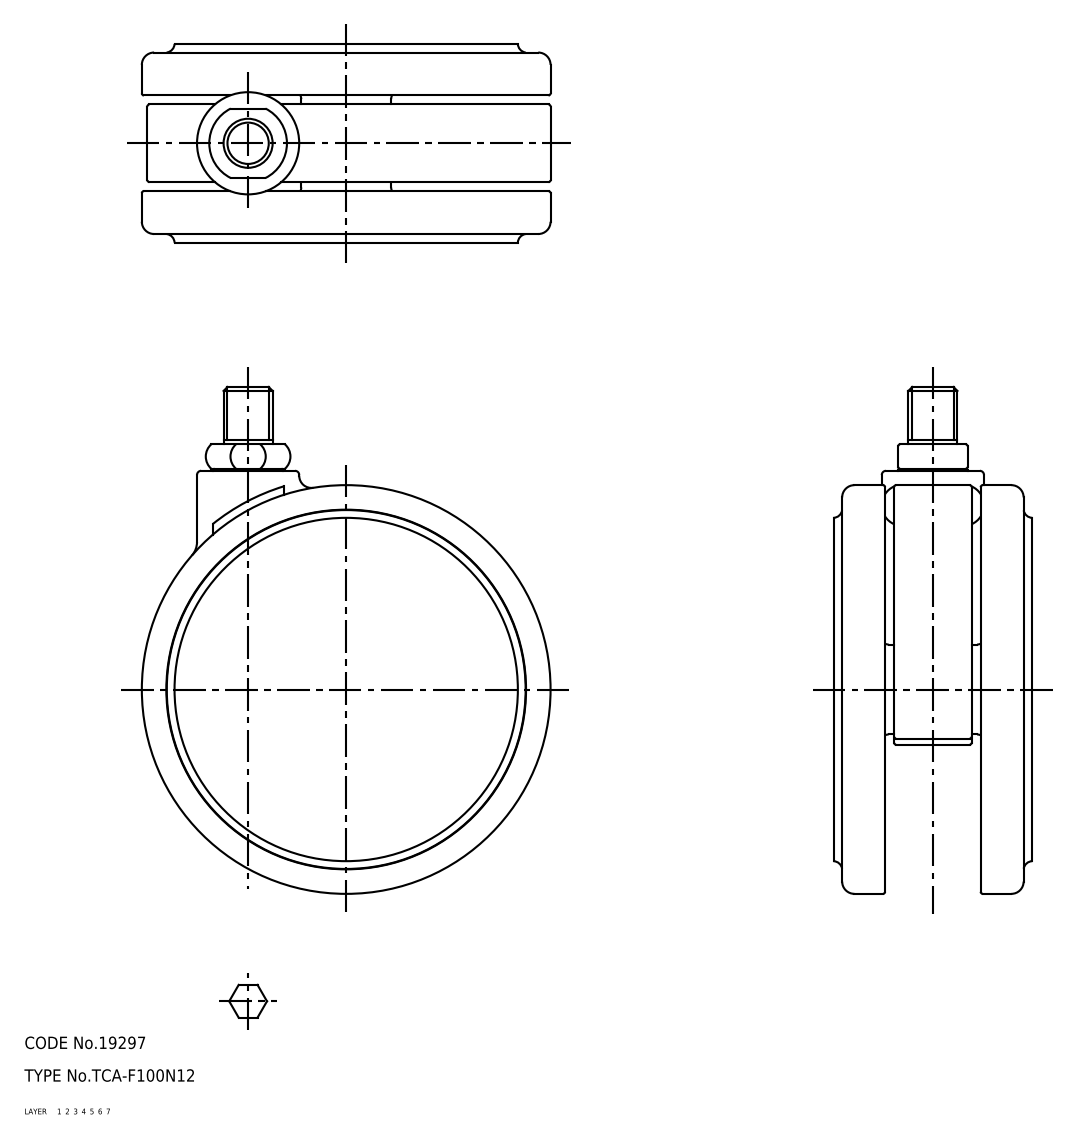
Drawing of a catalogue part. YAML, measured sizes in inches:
part_name: "caster; TCA-F100N12"
step_written_by: "SolidWorks 2015 (AUTOMOTIVE_DESIGN)"
units: inches
bodies: {solids: 1, faces: 999, planar: 379, cylindrical: 396, other: 224}
overall_size: [4.882, 3.937, 1.913]
volume: 10.8
surface_area: 138
round_holes:
  - {diameter: 0.314, count: 1}
  - {diameter: 0.318, count: 1}
  - {diameter: 0.366, count: 1}
  - {diameter: 0.421, count: 1}
  - {diameter: 0.484, count: 1}
  - {diameter: 0.512, count: 1}
  - {diameter: 0.945, count: 1}
  - {diameter: 3.189, count: 1}
  - {diameter: 3.465, count: 1}
round_bosses_or_shafts:
  - {diameter: 3.937, count: 1}
  - {diameter: 3.457, count: 1}
  - {diameter: 0.984, count: 1}
  - {diameter: 0.866, count: 1}
  - {diameter: 0.669, count: 1}
  - {diameter: 0.472, count: 1}
  - {diameter: 0.413, count: 1}
  - {diameter: 0.256, count: 1}
partial_cylinders:
  - {radius: 0.039, count: 30}
  - {radius: 0.02, count: 19}
  - {radius: 0.008, count: 16}
  - {radius: 0.079, count: 10}
  - {radius: 0.059, count: 9}
  - {radius: 0.118, count: 6}
  - {radius: 0.157, count: 1}
  - {radius: 0.315, count: 1}
face_to_face_distances: [0.071, 1.772, 1.843, 0.142, 1.701, 0.299, 0.496, 0.354, 0.425, 1.417]
